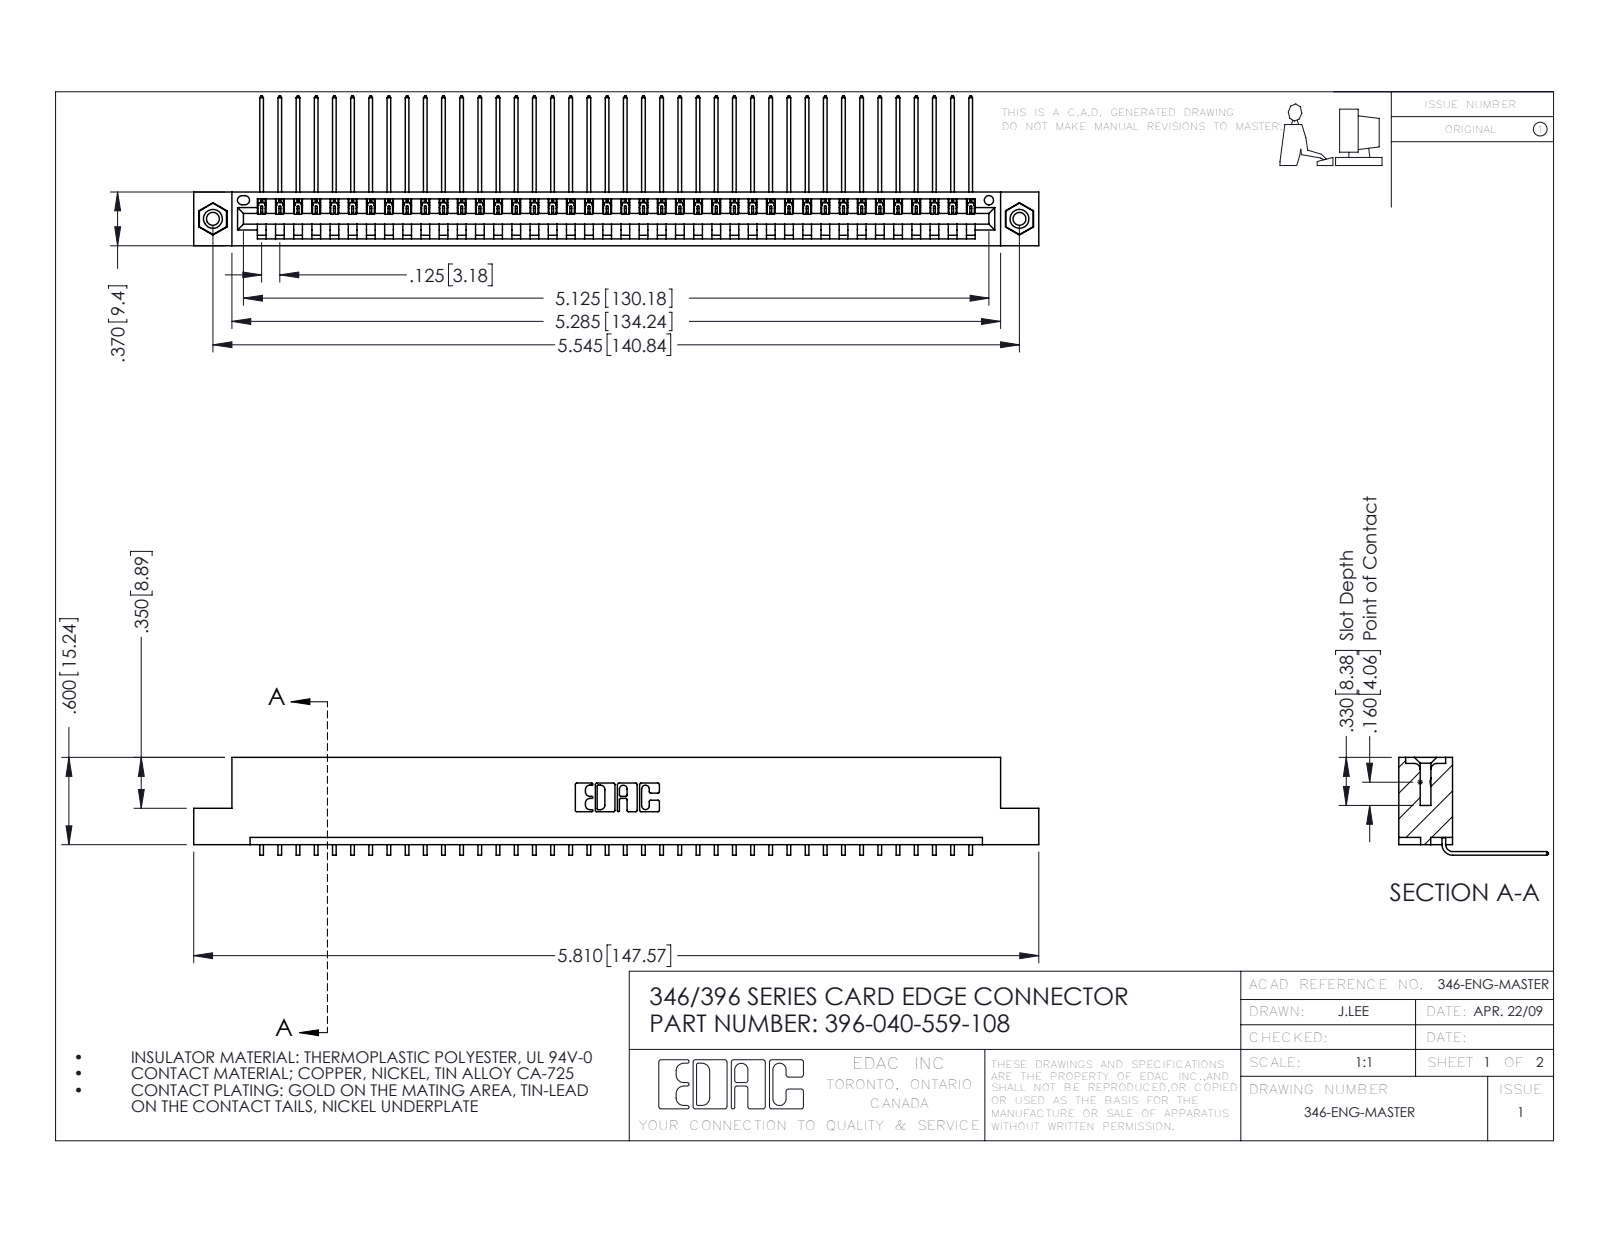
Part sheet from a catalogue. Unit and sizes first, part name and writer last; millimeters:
Units: millimetres
Overall size (bounding box): 147.6 × 26.2 × 17.1
Round holes (diameter × count): ⌀2.3 ×2, ⌀3.2 ×2, ⌀4 ×2, ⌀1.6 ×1
Round bosses / shafts (diameter × count): ⌀3.9 ×2
Partial cylindrical surfaces — rounded edges, fillets, slot ends (radius × count): R0.2 ×80, R0.3 ×22, R0.2 ×6, R0.8 ×6, R0.7 ×3, R0.8 ×2, R1 ×2, R0.4 ×1
Main face-to-face distances: 1.2, 8.2, 9.4, 0.6, 6.4, 1.8, 7.6, 3.8, 5.6, 2.5
Hole centre spacings: 6.2, 135.5, 140.8
Volume: 14 200 mm³ · Surface area: 18 590 mm²
Bodies: 43 solids, 2582 faces (1788 planar, 778 cylindrical, 16 other)
Part name (STEP PRODUCT): 345-292-001_558 559 Tail - 1; 396-040-559-108; 346 Part_Flush Mounting Lugs - 0.156 Dia-TI; 345-250-001_345-250-003-102
STEP written by: SolidWorks 2016 (CONFIG_CONTROL_DESIGN)
